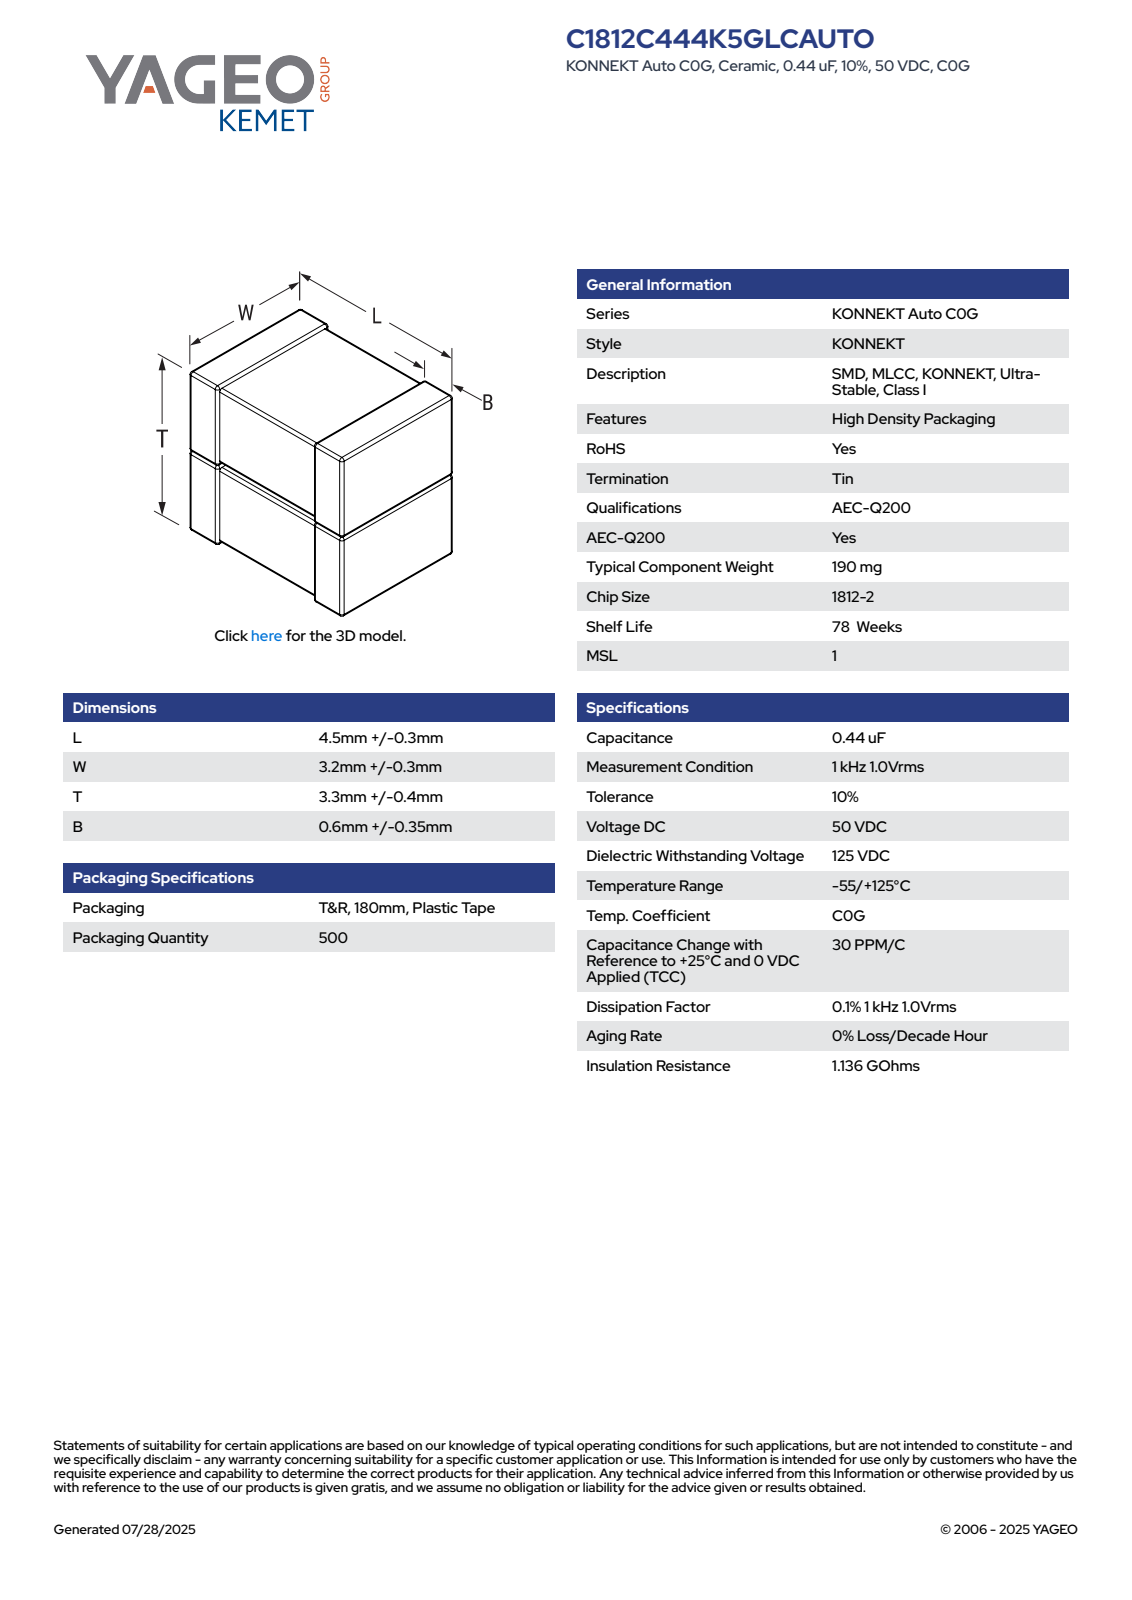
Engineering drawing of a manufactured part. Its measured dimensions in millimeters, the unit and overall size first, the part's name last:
Units: millimetres
Overall size (bounding box): 4.8 × 3.7 × 3.5
Main face-to-face distances: 1.85, 1.71, 4.8, 3.43, 1.78, 1.92, 3.63, 3.56, 3.36, 3.5
Volume: 58 mm³ · Surface area: 115 mm²
Bodies: 4 solids, 197 faces (81 planar, 84 cylindrical, 32 other)
Part name (STEP PRODUCT): CCSS_K2T_1812-2_L4.8W3.5B0.95T3.7
STEP written by: SolidWorks 2020 (AUTOMOTIVE_DESIGN)
